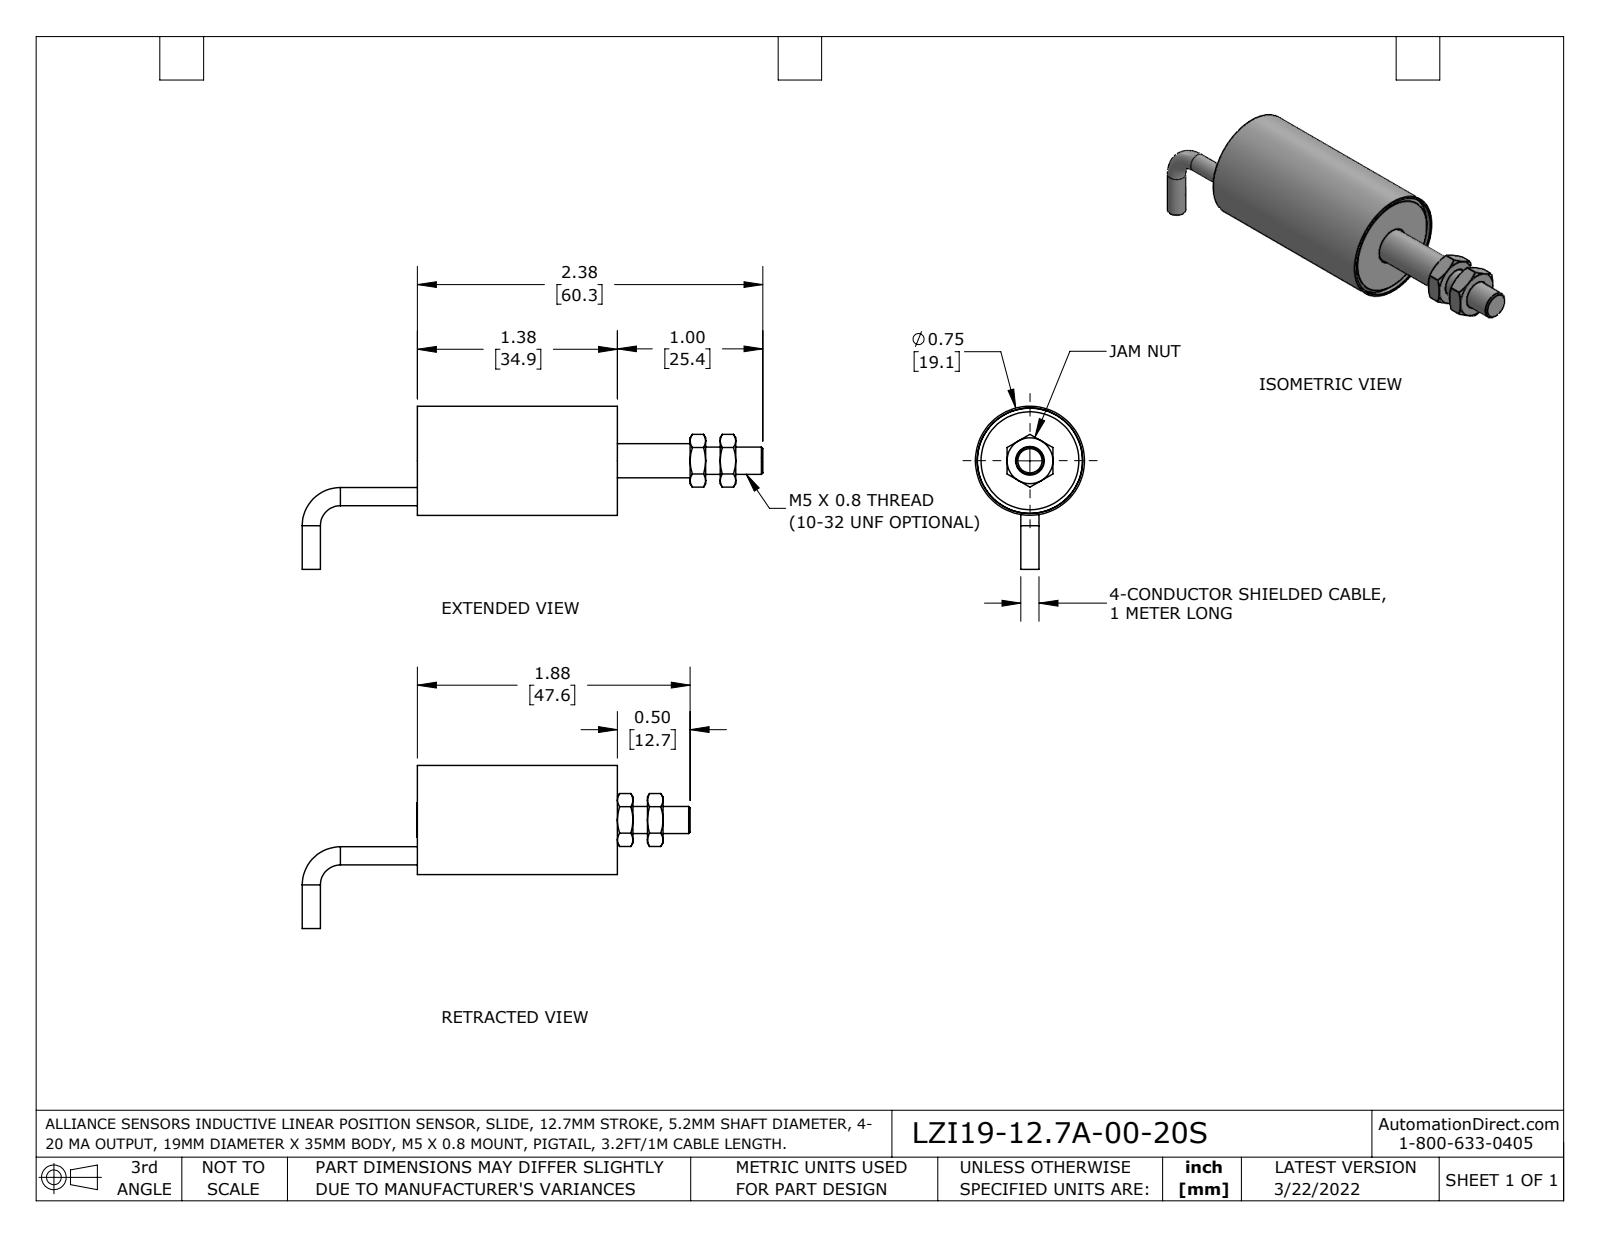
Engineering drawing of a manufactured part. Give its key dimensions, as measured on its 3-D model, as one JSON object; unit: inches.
{"part_name": "3100-0076_B18.2.4.5M - Hex jam nut, M5 x 0.8 --D-N; 3120-0006-06_-01-0Y; 3120-0007-ZY_with slot; 3120-0008-06_-01 (+6 more)", "step_written_by": "SolidWorks 2021 (AUTOMOTIVE_DESIGN)", "units": "inches", "bodies": {"solids": 10, "faces": 137, "planar": 42, "cylindrical": 44, "other": 51}, "overall_size": [3.168, 1.121, 0.75], "volume_in3": 0.3, "surface_area_in2": 15.45, "round_holes": [[0.165, 1], [0.188, 1], [0.197, 1], [0.234, 1], [0.281, 1], [0.68, 1], [0.725, 1]], "round_bosses_or_shafts": [[0.125, 2], [0.75, 1], [0.723, 1], [0.278, 1], [0.187, 1]], "partial_cylinders_radius": [[0.052, 1]], "face_to_face_distances": [0.06, 1.295, 0.08, 1.235, 1.355, 0.315, 0.206, 0.106, 0.374, 0.1]}
